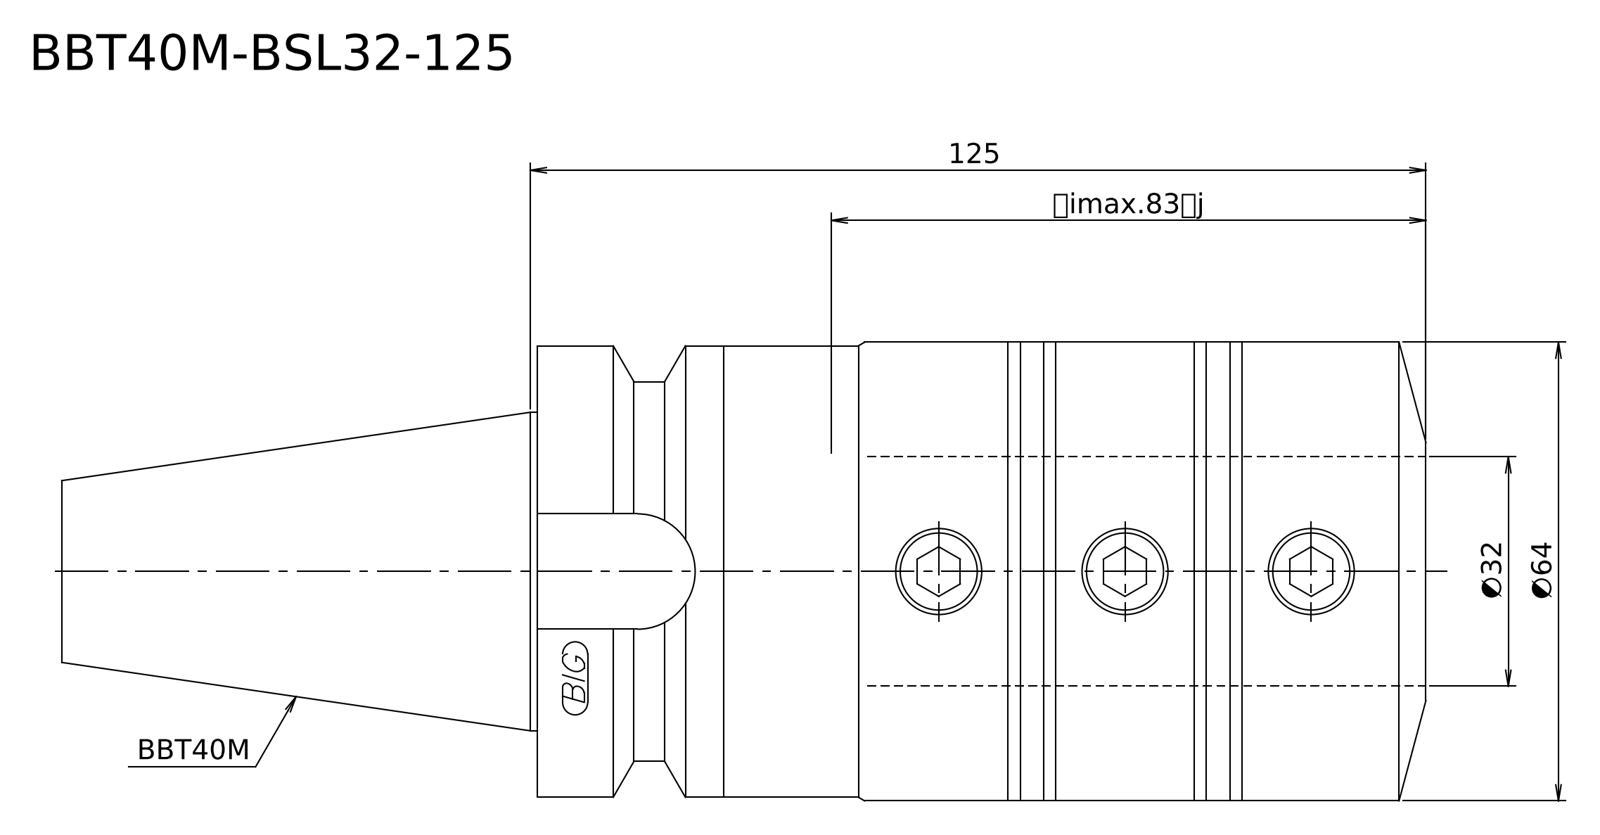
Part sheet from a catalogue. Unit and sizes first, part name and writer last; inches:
Units: inches
Overall size (bounding box): 7.496 × 2.52 × 2.52
Round bosses / shafts (diameter × count): ⌀2.52 ×1, ⌀2.48 ×1, ⌀2.087 ×1, ⌀1.75 ×1
Main face-to-face distances: 4.882, 7.496, 2.614
Volume: 27.4 in³ · Surface area: 58.35 in²
Bodies: 1 solid, 13 faces (3 planar, 5 cylindrical, 5 other)
STEP written by: Kubotek KeyCreator V8.5.1 (14335) (CONFIG_CONTROL_DESIGN)
